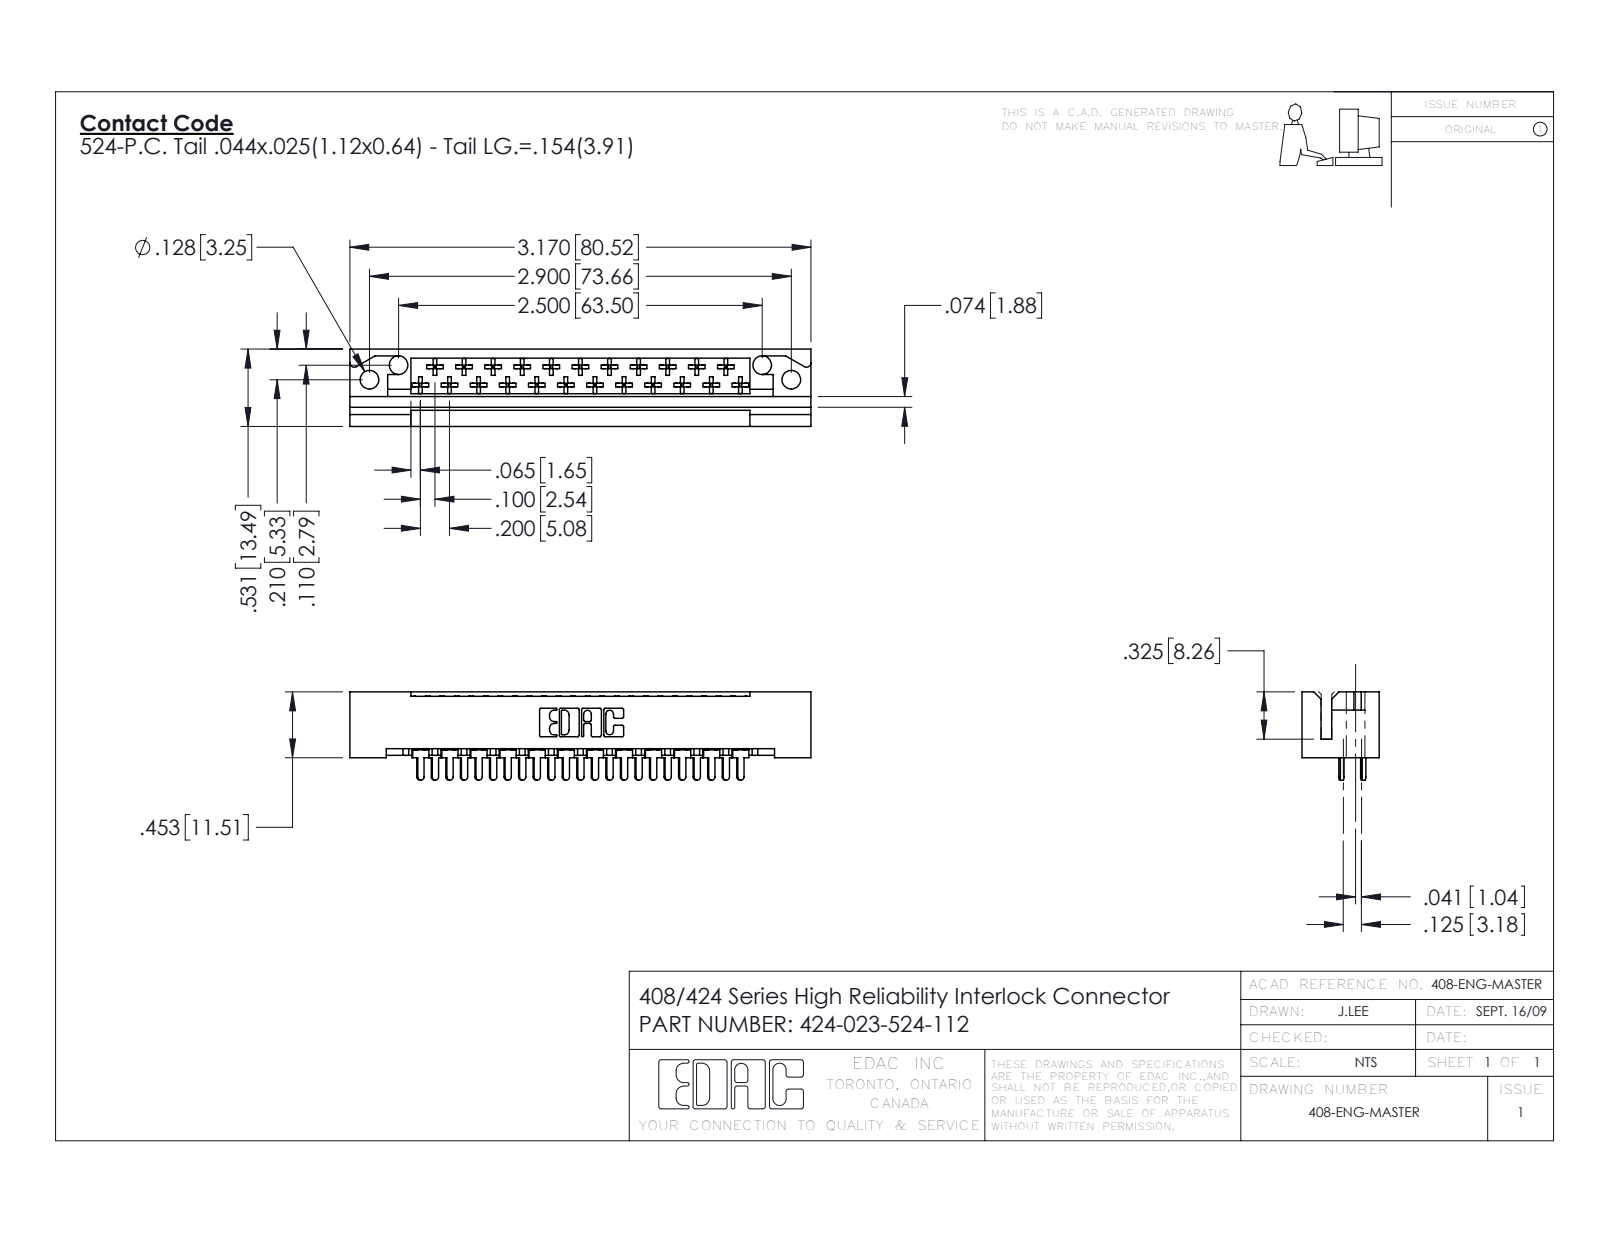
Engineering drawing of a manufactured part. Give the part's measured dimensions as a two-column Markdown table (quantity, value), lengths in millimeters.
| quantity | value |
| --- | --- |
| part name | 424 Part_023; 424-023-524-112; 408-290-001_408-290-124 - Bottom; 408-290-001_408-290-124 - Top |
| STEP written by | SolidWorks 2016 (CONFIG_CONTROL_DESIGN) |
| units | millimeters |
| bodies | 24 solids, 1410 faces (1055 planar, 263 cylindrical, 92 other) |
| overall size | 80.5 × 15.4 × 13.5 |
| volume | 8 770 mm³ |
| surface area | 10 600 mm² |
| round holes (diameter × count) | 3.3 × 4 |
| partial cylindrical surfaces (radius × count) | 0.3 × 138, 0.5 × 25, 0.6 × 23, 0.3 × 22, 0.2 × 6, 0.8 × 6, 0.7 × 3, 0.8 × 2 |
| main face-to-face distances | 10.2, 0.6, 13.5, 3.2, 2.5, 3.3, 0.6, 8.3, 1.9, 5.2 |
| hole center spacings | 5.7, 68.6, 63.5, 73.7 |
